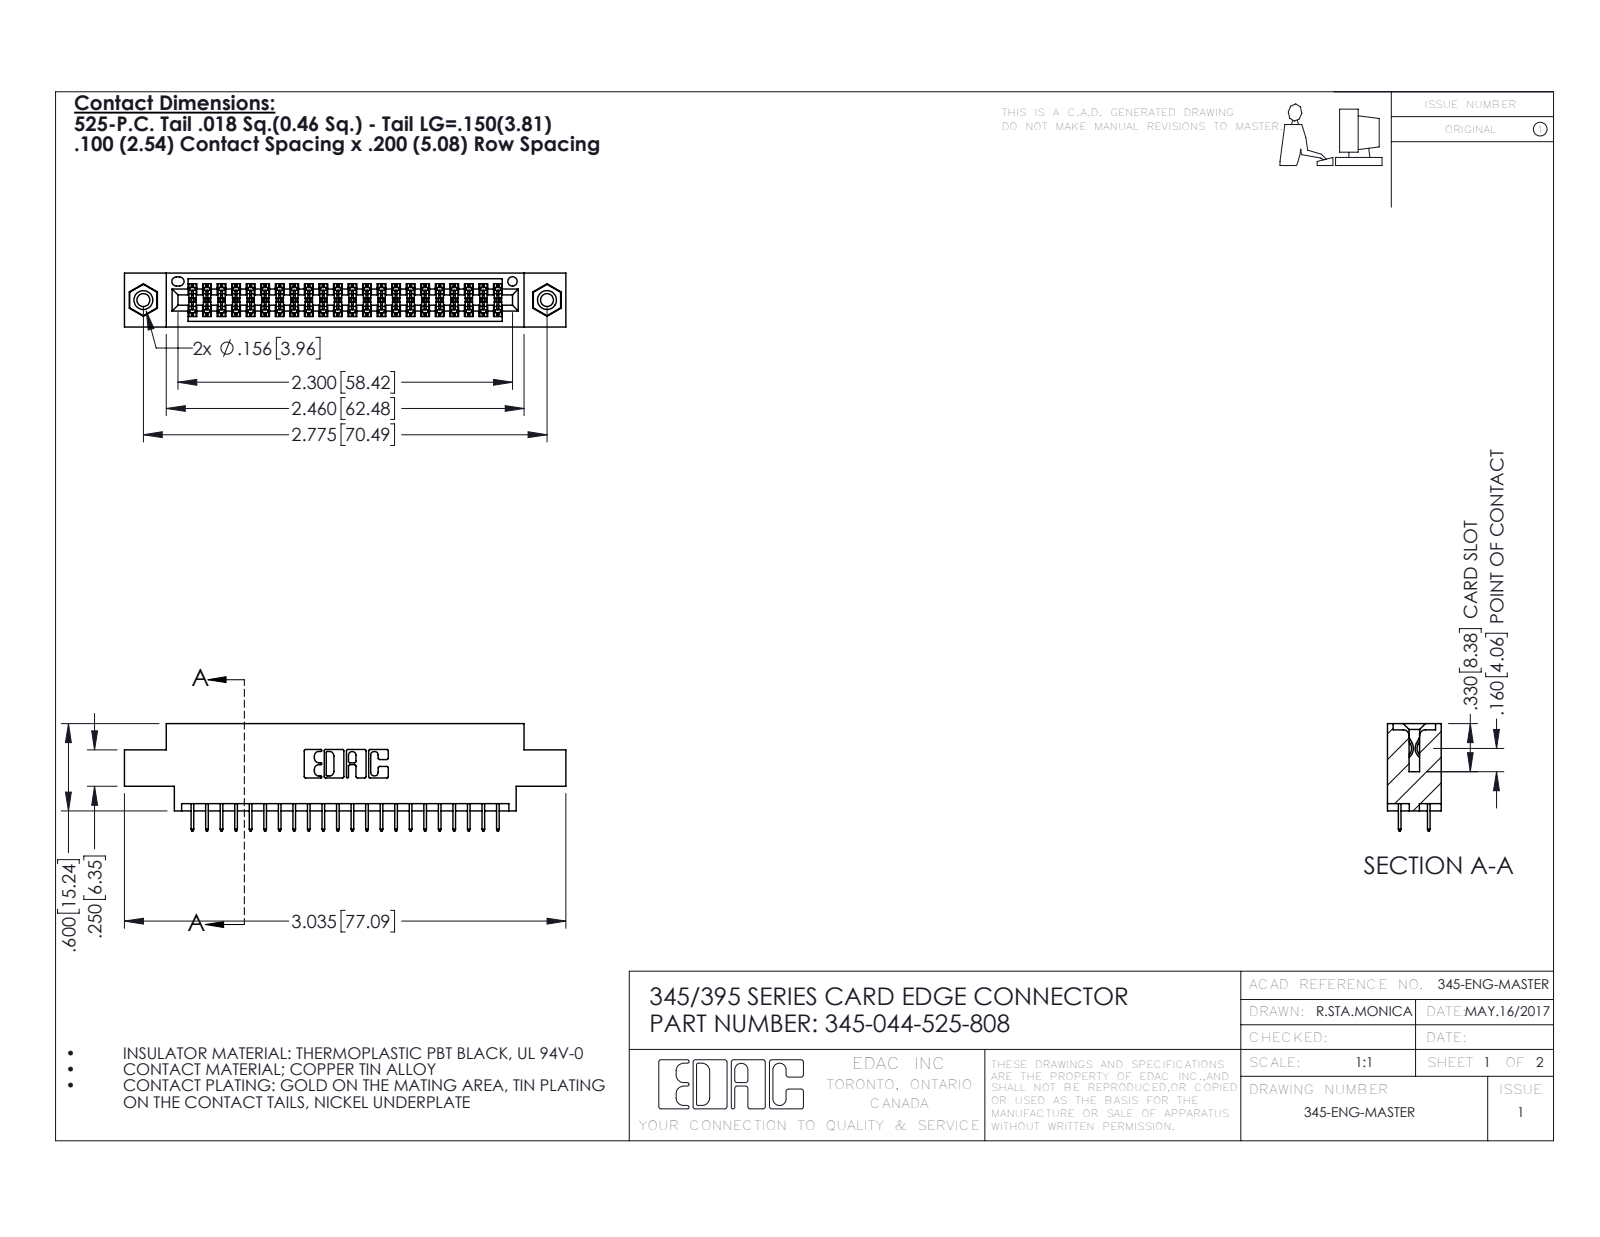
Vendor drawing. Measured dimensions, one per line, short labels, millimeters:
name: 345-292-001_345-293-125; 345-250-001_345-250-003-102; 345 Part_0.170 Offset - 0.156 Dia-TI; 345-044-525-808
written by: SolidWorks 2020 (CONFIG_CONTROL_DESIGN)
unit: mm
bodies: 47 solids, 2566 faces (1832 planar, 718 cylindrical, 16 other)
size: 77.1 × 18.7 × 9.4
volume: 7 110 mm³; area: 10 060 mm²
holes: 2× ⌀2.3, 2× ⌀3.2, 2× ⌀4, 1× ⌀1.6
bosses: 2× ⌀3.9
rounds: 66× R0.2, 22× R0.3, 6× R0.2, 6× R0.8, 3× R0.7, 2× R0.4, 2× R0.5, 2× R0.6
face distances: 1.8, 7.6, 9.4, 5.1, 2.5, 6.9, 0.6, 5.7, 4.4, 1.8
hole spacings: 6.9, 64.5, 70.5
